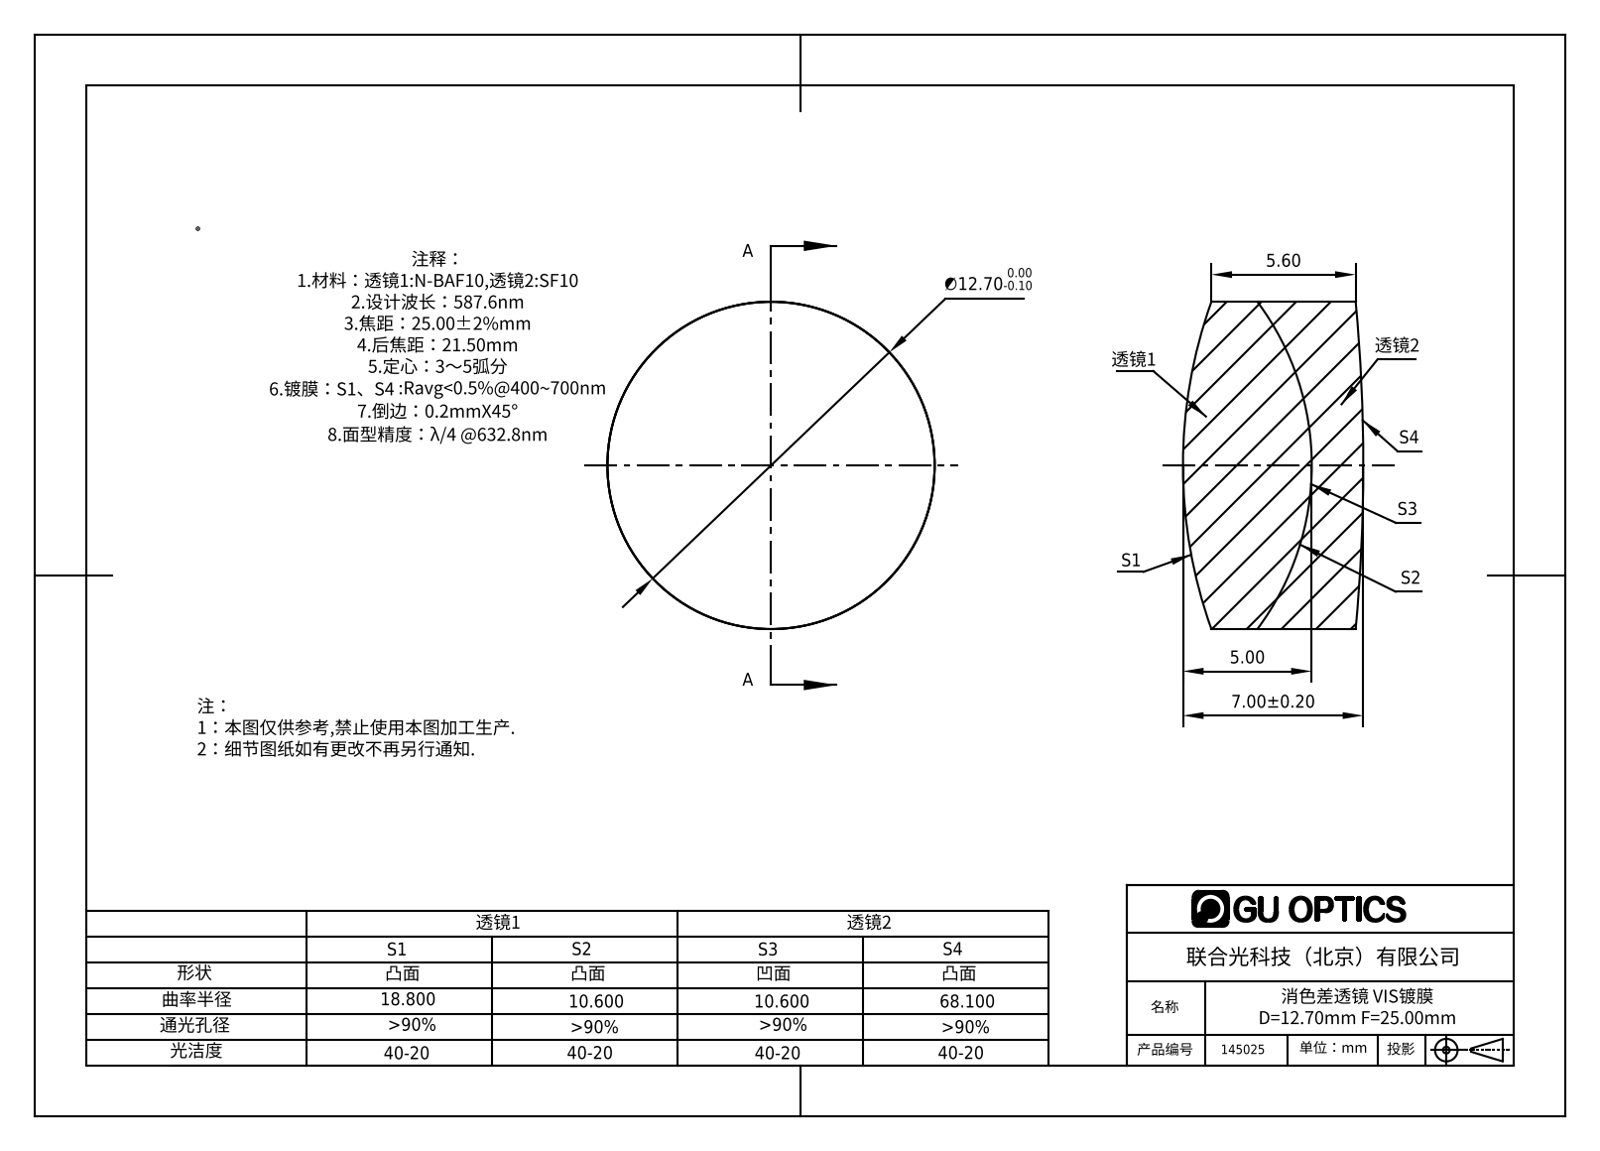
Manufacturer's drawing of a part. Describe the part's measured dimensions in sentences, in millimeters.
The part is named "145025". Its 3-D file was written by "SolidWorks 2016 (AUTOMOTIVE_DESIGN)". It is 2 solids with 12 faces: 0 planar, 4 cylindrical and 8 other. Overall it measures 12.7 by 12.7 by 7 millimeters. Its volume is 799 cubic millimeters and its surface area 762 square millimeters. Round bosses or shafts: 1 of diameter 12.7.
